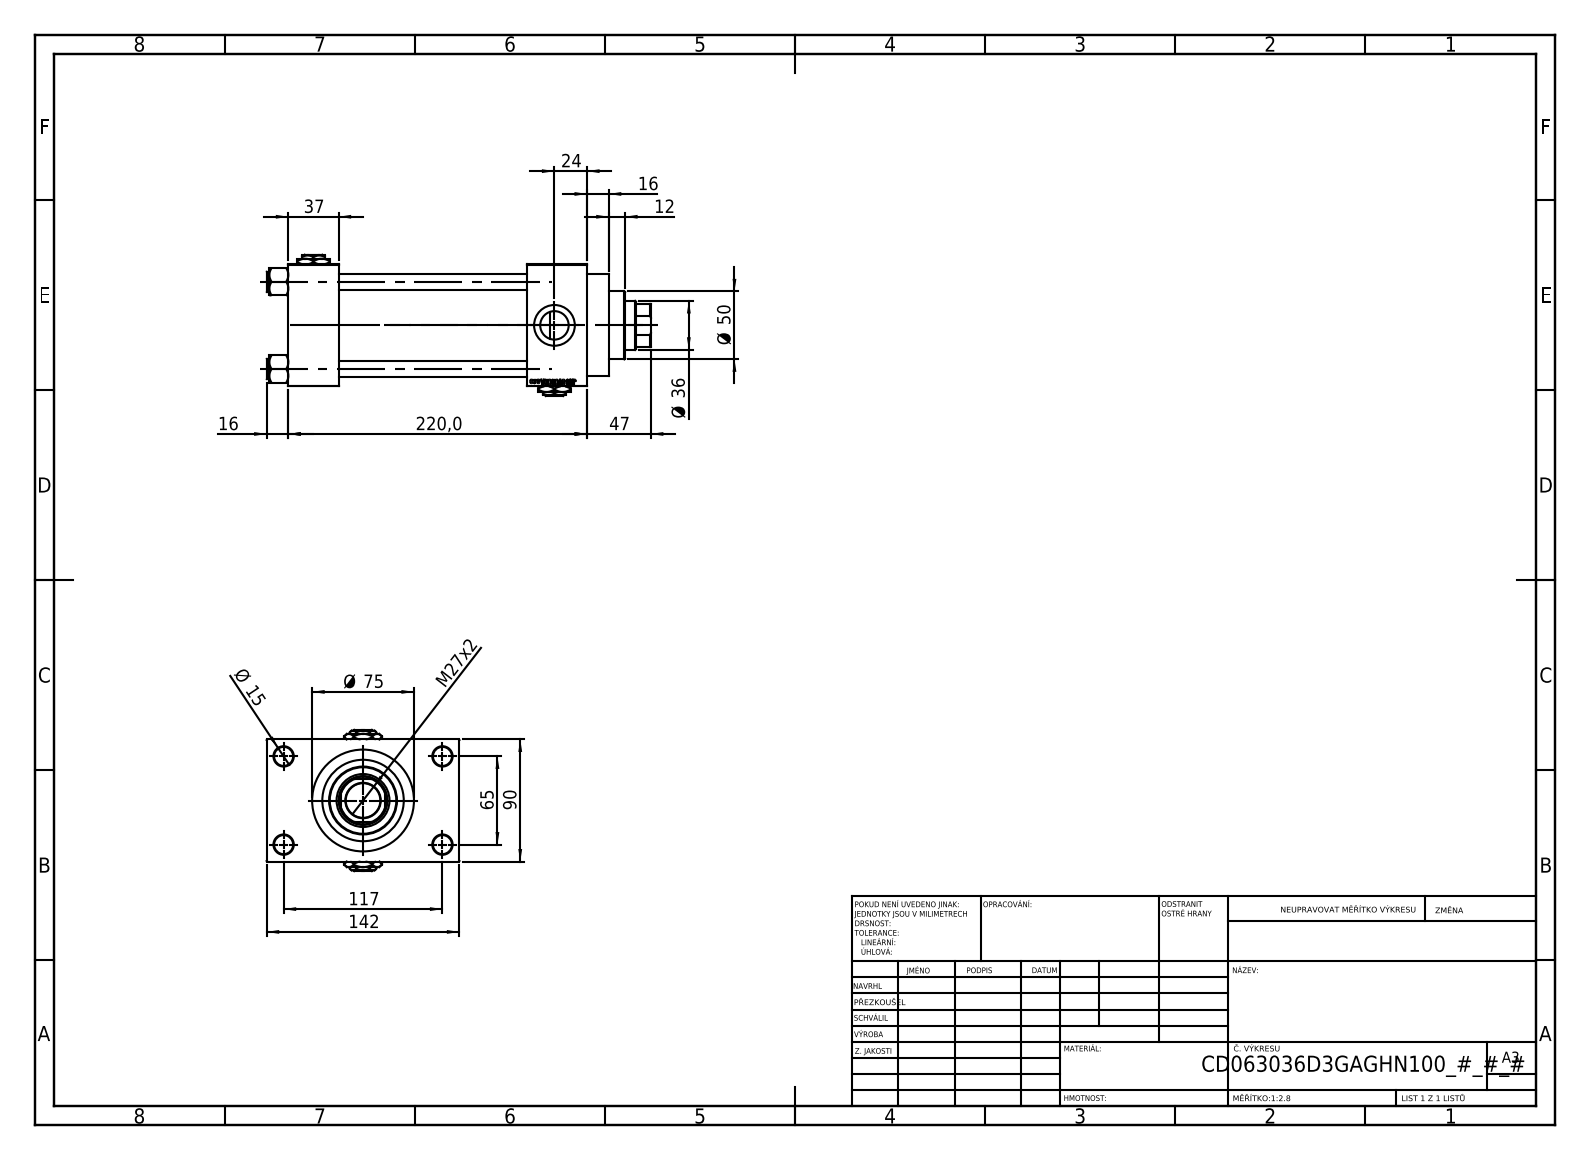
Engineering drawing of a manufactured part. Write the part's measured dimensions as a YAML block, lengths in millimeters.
part_name: "V215CD_VC_A; V215CD_D_Body; V215CD_D_TYCINKA; Zatka_pro_OIL_PORT (+2 more)"
step_written_by: "SolidWorks 2019 (CONFIG_CONTROL_DESIGN)"
units: millimeters
bodies: {solids: 13, faces: 1194, planar: 543, cylindrical: 93, other: 558}
overall_size: [283, 142, 104]
volume: 1278000
surface_area: 263396
round_holes:
  - {diameter: 12, count: 4}
  - {diameter: 14, count: 4}
  - {diameter: 20.96, count: 3}
  - {diameter: 30, count: 3}
  - {diameter: 7, count: 2}
  - {diameter: 25.5, count: 1}
  - {diameter: 36, count: 1}
  - {diameter: 39, count: 1}
  - {diameter: 50, count: 1}
  - {diameter: 60, count: 1}
  - {diameter: 63, count: 1}
round_bosses_or_shafts:
  - {diameter: 15, count: 4}
  - {diameter: 75, count: 1}
  - {diameter: 69, count: 1}
partial_cylinders:
  - {radius: 17.5, count: 1}
face_to_face_distances: [90, 139, 37, 176, 220, 183, 44, 26, 116, 142]
hole_center_spacings: [26.35, 45.47, 64.3, 66.92, 69.81, 90.65, 111.34, 65]
